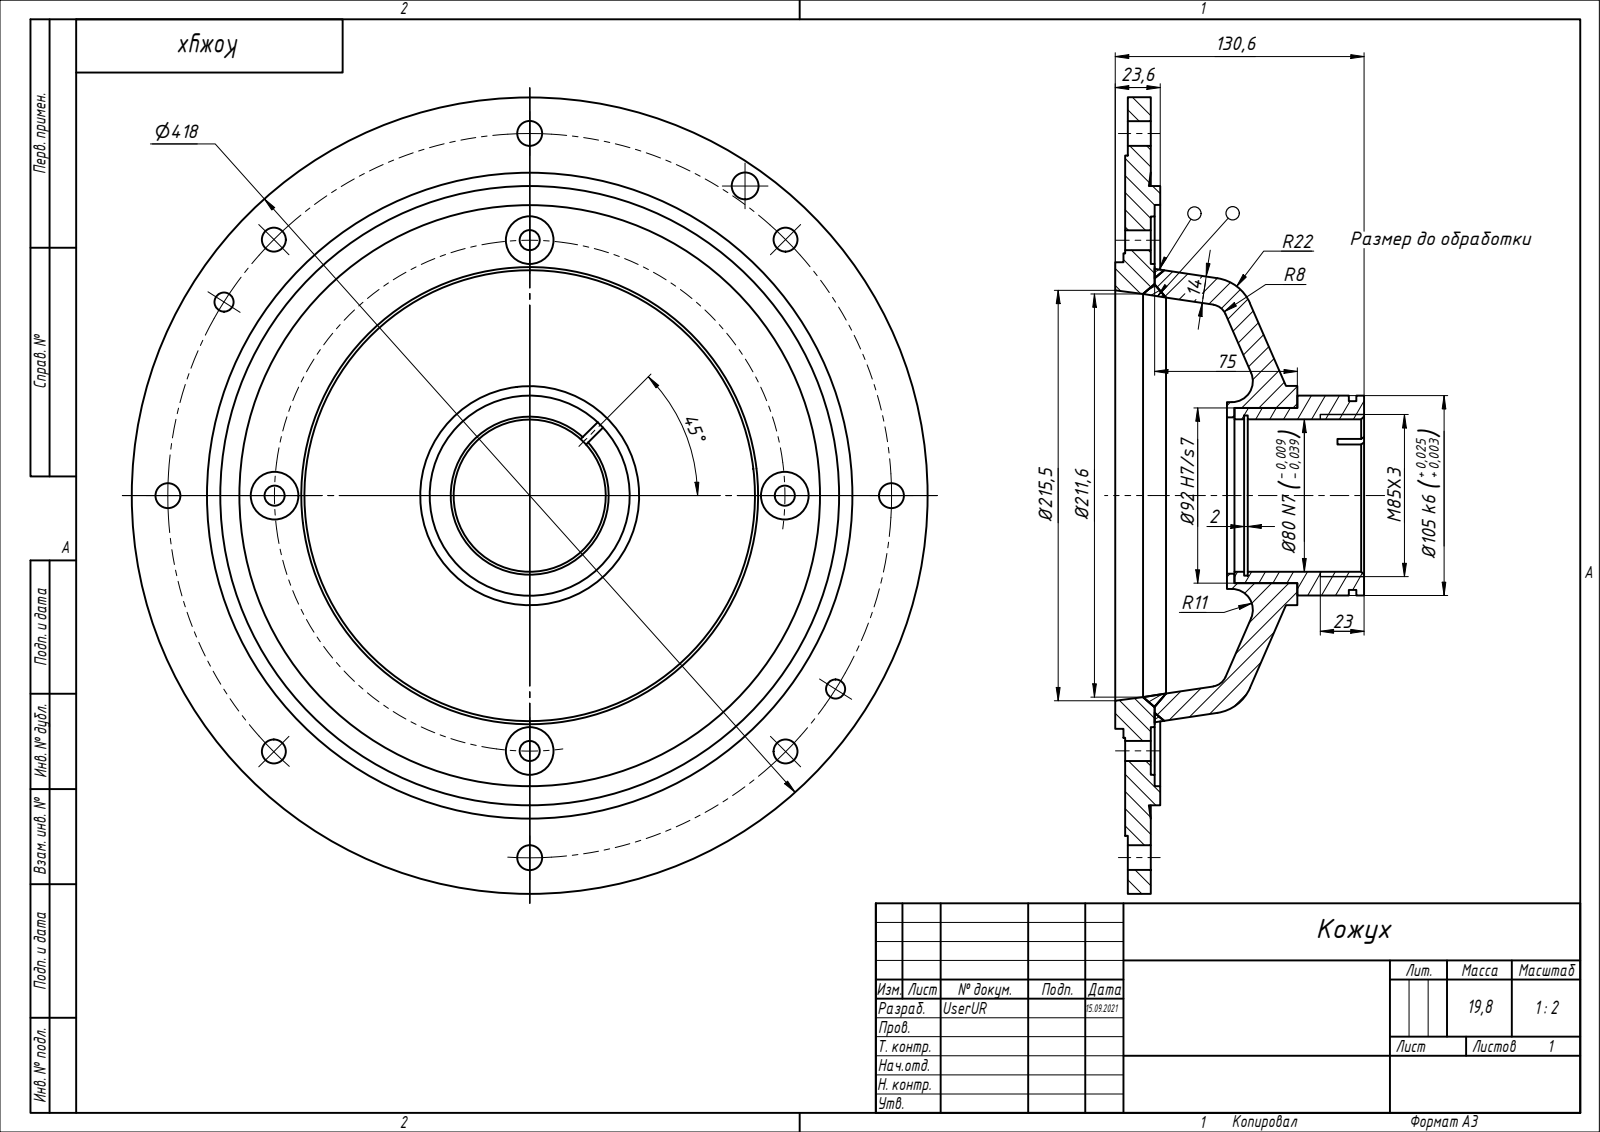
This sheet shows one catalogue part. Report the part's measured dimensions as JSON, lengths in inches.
{"part_name": "ПТРВ.745535.001 Кожух", "step_written_by": "SolidWorks 2018 (AUTOMOTIVE_DESIGN)", "units": "inches", "bodies": {"solids": 1, "faces": 18610, "planar": 18428, "cylindrical": 174, "other": 8}, "overall_size": [22.323, 16.614, 10.394], "volume_in3": 42.58, "surface_area_in2": 2269, "round_holes": [[0.098, 26], [0.28, 4]], "partial_cylinders_radius": [[0.067, 8], [0.12, 8], [0.155, 8], [0.079, 6], [0.098, 6], [0.118, 4], [0.124, 4], [0.138, 4]], "face_to_face_distances": [0.039, 10.311, 10.35, 10.272, 16.575, 16.535, 16.614, 0.197, 10.114, 0.044], "hole_center_spacings": [0.772, 1.543, 2.315, 3.087, 3.858, 4.63, 5.402, 6.173]}
